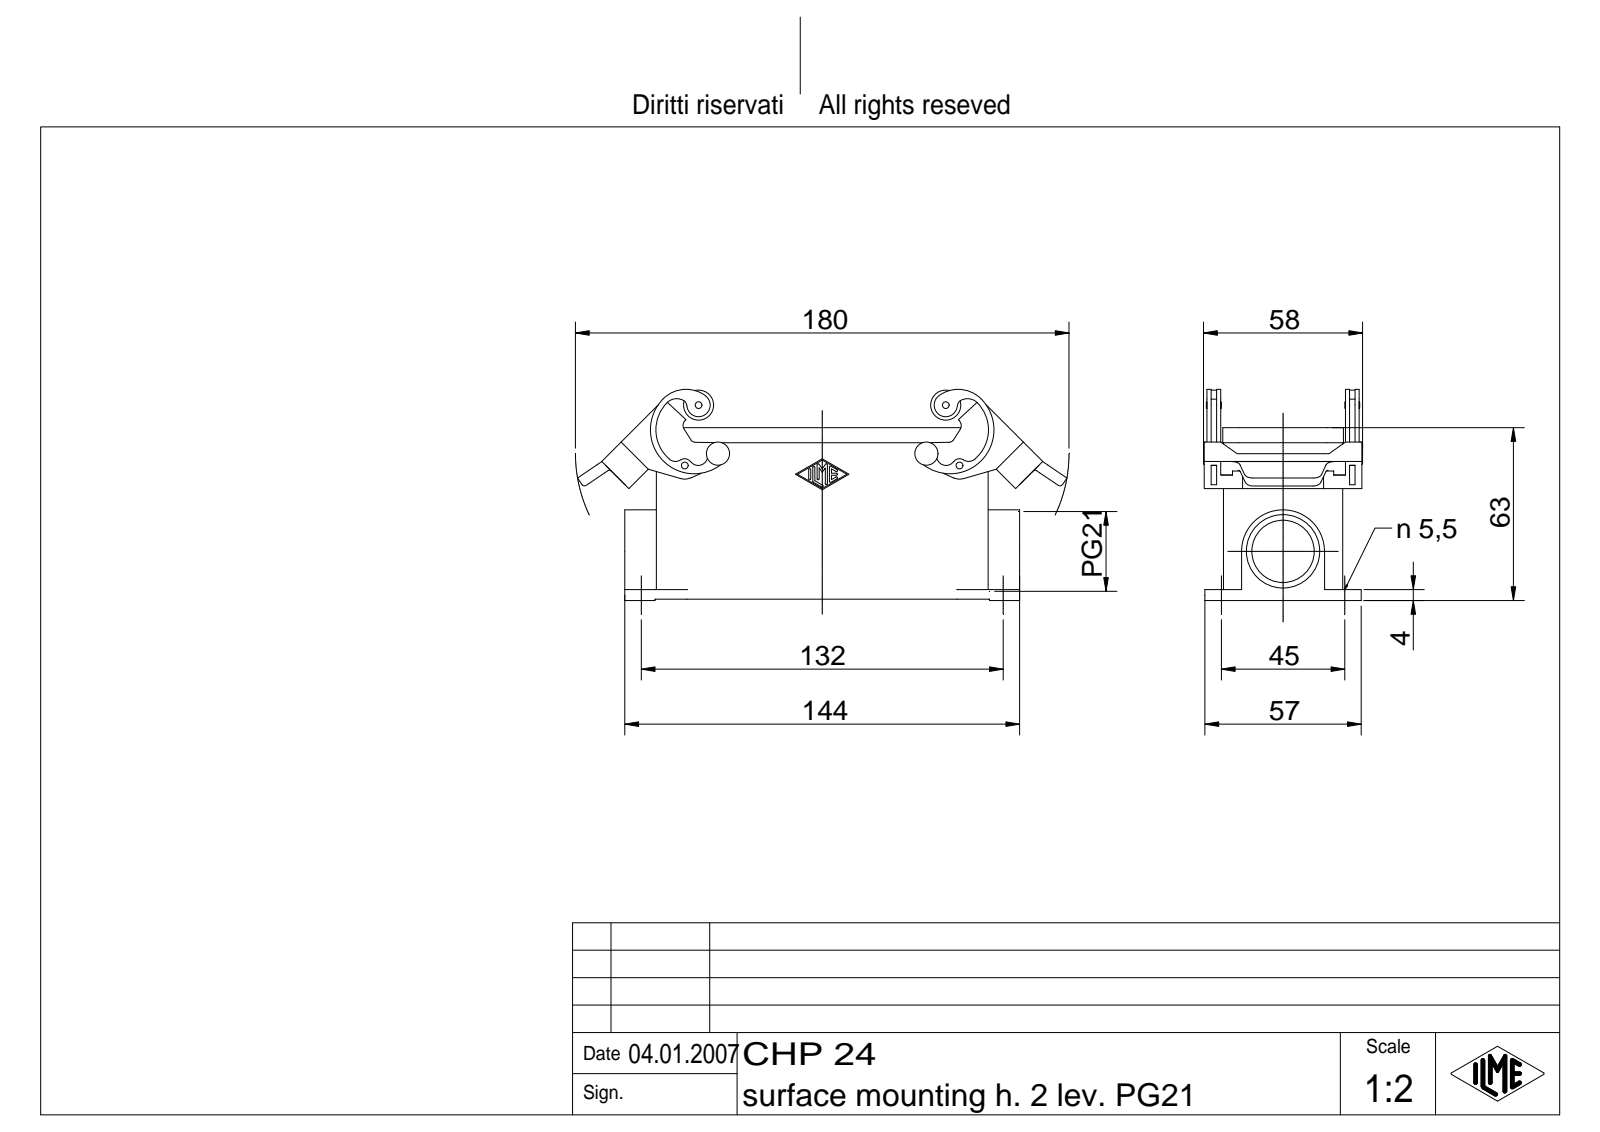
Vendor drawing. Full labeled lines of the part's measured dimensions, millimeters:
Part name (STEP PRODUCT): CHP 24
STEP written by: Autodesk Inventor 7 (AUTOMOTIVE_DESIGN)
Units: millimetres
Bodies: 1 solid, 749 faces (191 planar, 205 cylindrical, 353 other)
Overall size (bounding box): 178.49 × 76.94 × 58
Volume: 120 760 mm³ · Surface area: 71 190 mm²
Round holes (diameter × count): ⌀2 ×4, ⌀5.5 ×4, ⌀2.5 ×2, ⌀22.78 ×1, ⌀26.78 ×1
Round bosses / shafts (diameter × count): ⌀11 ×2, ⌀5 ×2, ⌀3 ×2
Partial cylindrical surfaces — rounded edges, fillets, slot ends (radius × count): R1 ×20, R0.38 ×14, R3 ×12, R6 ×8, R2.5 ×6, R1.5 ×4, R2 ×4, R3.5 ×4
Main face-to-face distances: 3, 40.5, 43.5, 37.5, 3.5, 4, 0.75, 50.5, 40.75, 3.75
Hole centre spacings: 22.56, 45, 97.67, 132, 139.46, 90.14, 100.18
